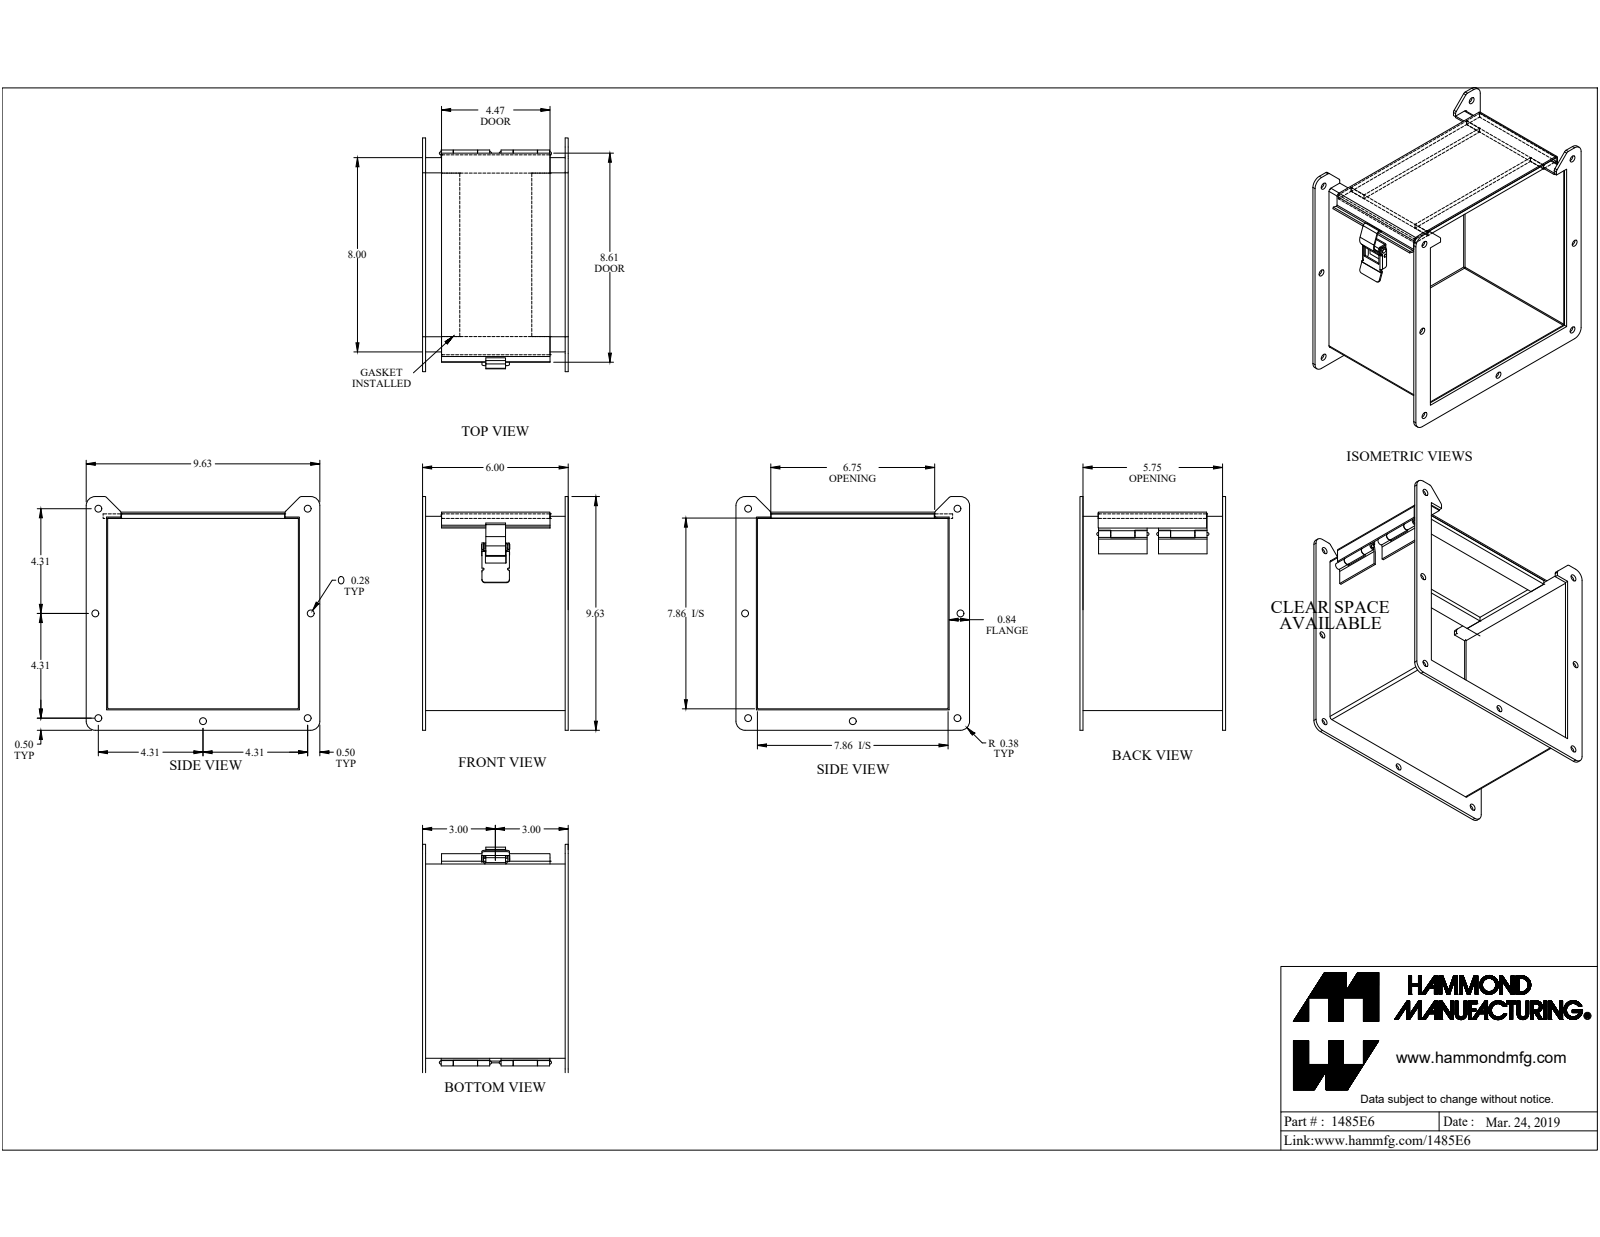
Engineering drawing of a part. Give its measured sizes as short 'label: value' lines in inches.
name: 1485E6
written by: SolidWorks 2019 (CONFIG_CONTROL_DESIGN)
unit: in
bodies: 17 solids, 302 faces (188 planar, 110 cylindrical, 4 other)
size: 9.625 × 9.625 × 6
volume: 23.18 in³; area: 559.4 in²
holes: 7× ⌀0.281, 1× ⌀0.125, 1× ⌀0.13, 1× ⌀0.164
bosses: 2× ⌀0.187, 1× ⌀0.275, 1× ⌀0.156, 1× ⌀0.125, 1× ⌀0.125
rounds: 7× R0.016, 7× R0.036, 7× R0.108, 7× R0.125, 4× R0.375, 3× R0.035, 3× R0.039, 3× R0.076
face distances: 0.072, 7.928, 8.1, 8, 7.856, 0.125, 5.875, 8.028, 8.172, 6
hole spacings: 8.625, 4.314, 4.315, 9.755, 9.755, 12.197, 0.285, 1.054
